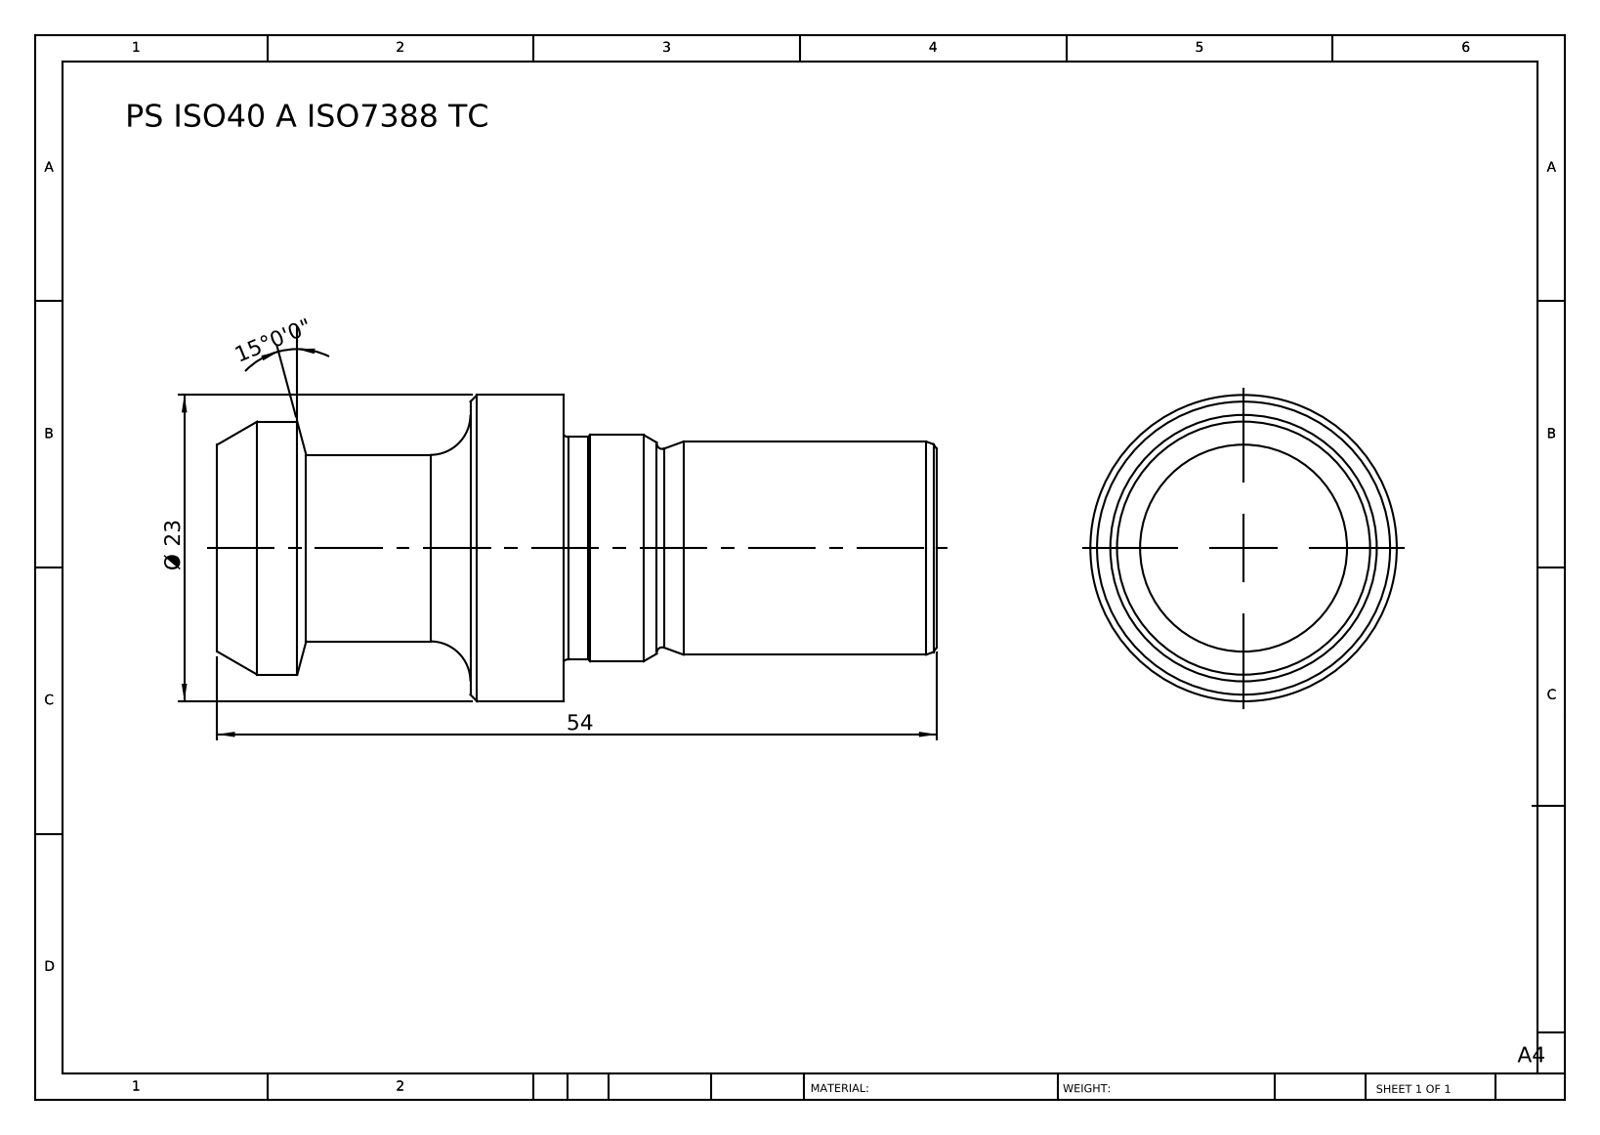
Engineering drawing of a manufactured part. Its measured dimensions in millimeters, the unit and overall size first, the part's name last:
Units: millimetres
Overall size (bounding box): 54 × 23 × 23
Round bosses / shafts (diameter × count): ⌀23 ×1, ⌀19 ×1, ⌀17 ×1, ⌀16.7 ×1, ⌀16 ×1, ⌀14 ×1
Main face-to-face distances: 54, 28, 26, 7, 35, 19, 21, 14, 33
Volume: 12 328 mm³ · Surface area: 3 758 mm²
Bodies: 1 solid, 43 faces (5 planar, 12 cylindrical, 26 other)
Part name (STEP PRODUCT): PS ISO40 A ISO7388 TC
STEP written by: SolidWorks 2014 (CONFIG_CONTROL_DESIGN)
